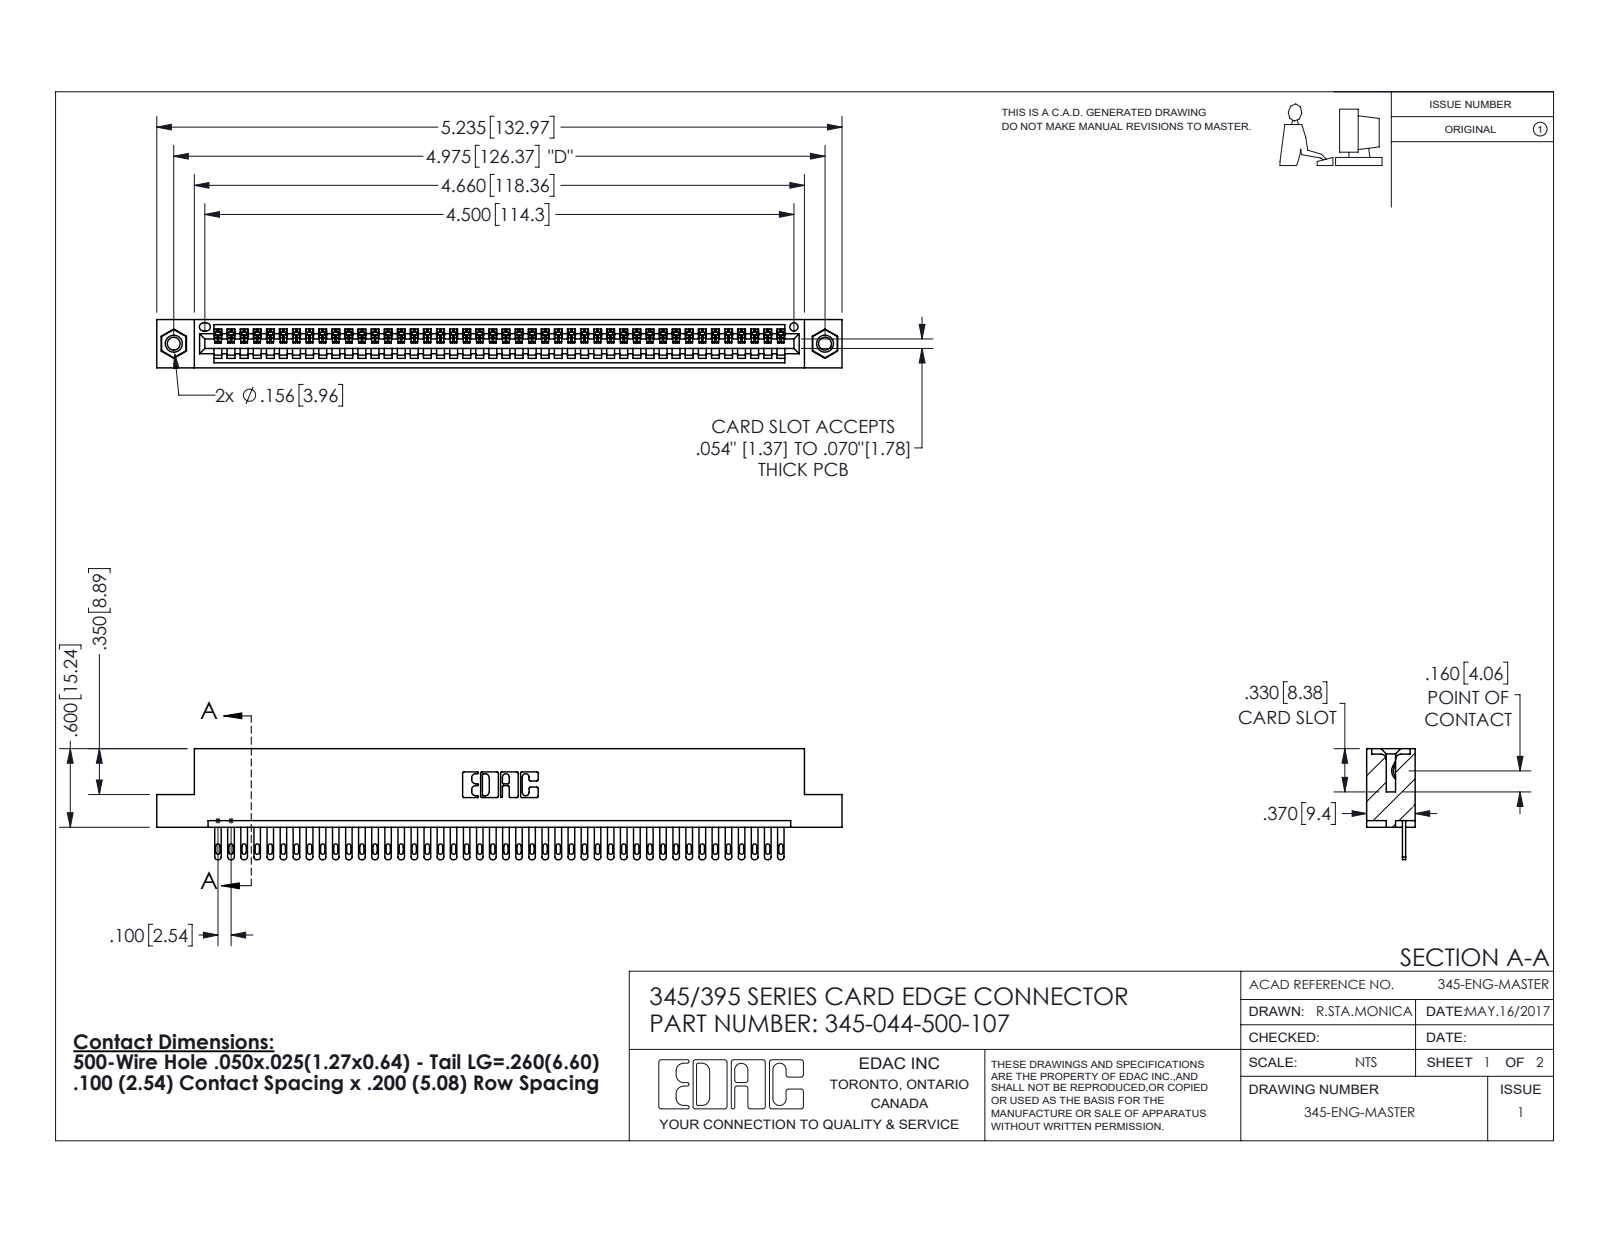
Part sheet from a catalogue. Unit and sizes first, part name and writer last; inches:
Units: inches
Overall size (bounding box): 5.235 × 0.847 × 0.37
Round holes (diameter × count): ⌀0.098 ×2, ⌀0.125 ×2, ⌀0.156 ×2, ⌀0.064 ×1
Round bosses / shafts (diameter × count): ⌀0.155 ×2
Partial cylindrical surfaces — rounded edges, fillets, slot ends (radius × count): R0.006 ×88, R0.016 ×88, R0.02 ×88, R0.01 ×22, R0.007 ×6, R0.031 ×6, R0.026 ×3, R0.031 ×2
Main face-to-face distances: 0.072, 0.298, 0.37, 0.2, 0.098, 0.272, 0.025, 0.225, 0.149, 0.072
Hole centre spacings: 0.27, 4.739, 4.975
Volume: 0.773 in³ · Surface area: 26.32 in²
Bodies: 47 solids, 2562 faces (1608 planar, 938 cylindrical, 16 other)
Part name (STEP PRODUCT): 345-044-500-107; 345-250-001_345-250-005-103; 345 Part_Flush Mounting Lugs - 0.156 Dia-TI; 345-292-001_345-293-100
STEP written by: SolidWorks 2016 (CONFIG_CONTROL_DESIGN)
